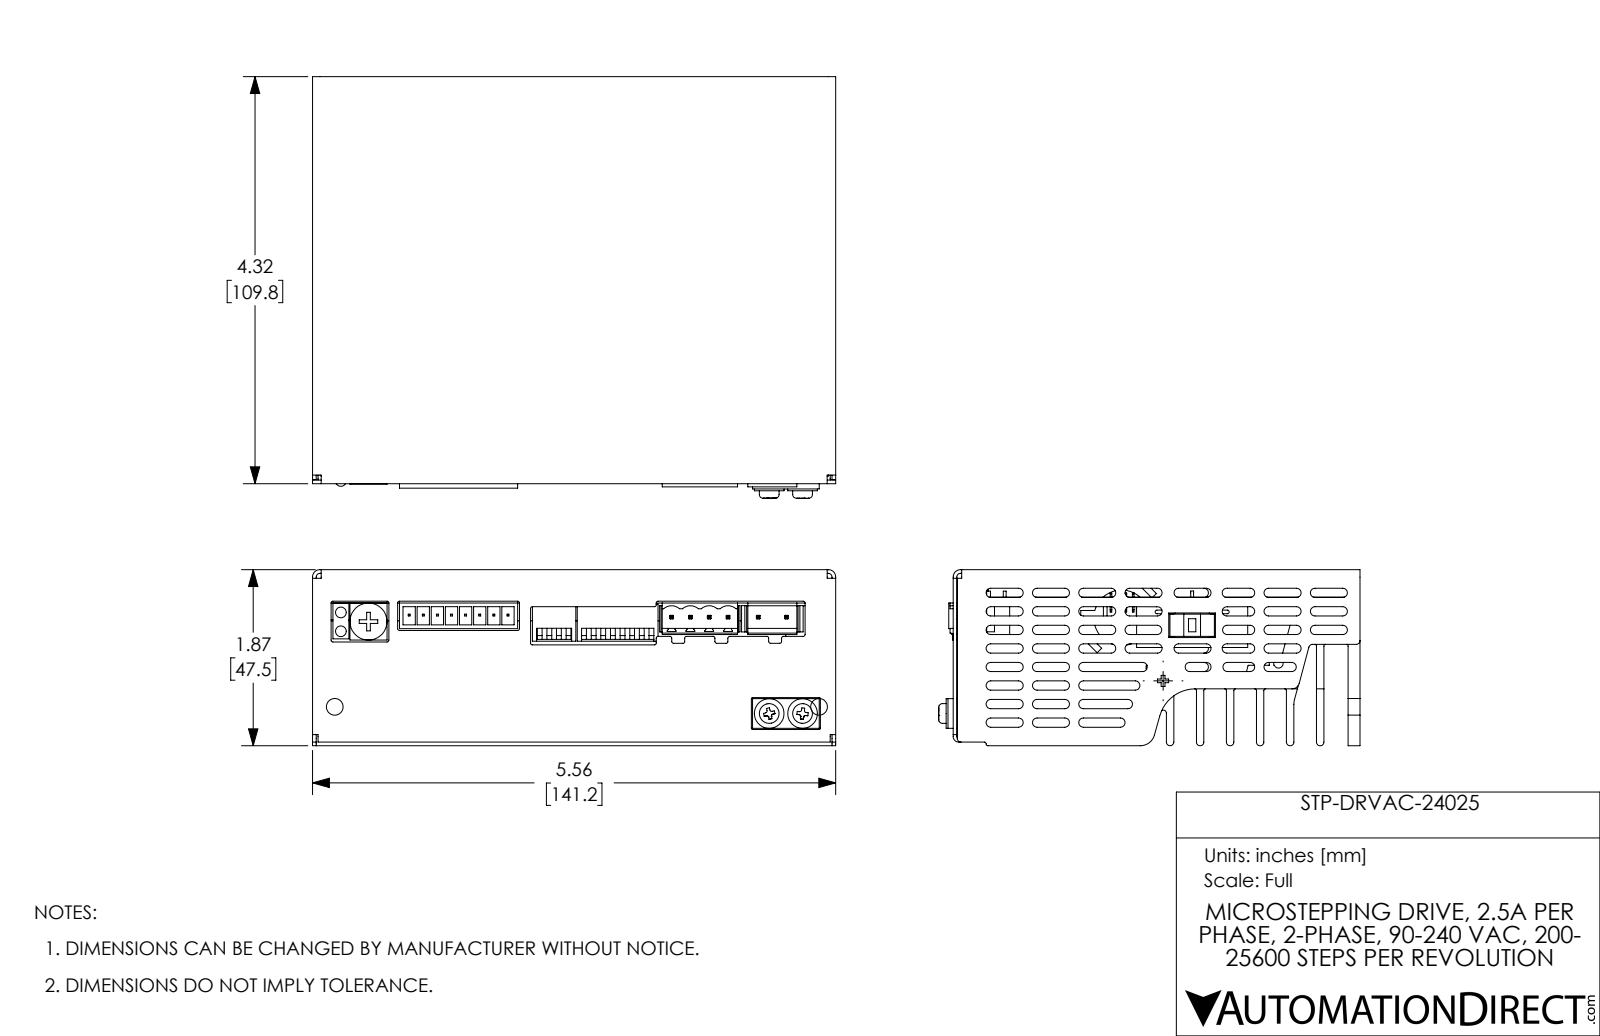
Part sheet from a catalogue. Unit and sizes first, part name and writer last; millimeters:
Units: millimetres
Overall size (bounding box): 141.2 × 113.7 × 47.5
Round holes (diameter × count): ⌀0.8 ×42, ⌀2.5 ×10, ⌀3.2 ×8, ⌀1.6 ×6, ⌀3 ×5, ⌀1 ×4, ⌀4.5 ×1, ⌀5.7 ×1, ⌀15 ×1
Round bosses / shafts (diameter × count): ⌀0.5 ×6, ⌀8 ×2, ⌀2.9 ×2, ⌀10 ×1
Partial cylindrical surfaces — rounded edges, fillets, slot ends (radius × count): R1.2 ×102, R0.5 ×90, R1 ×14, R0.2 ×10, R0.6 ×6, R0.6 ×6, R0.3 ×4, R2 ×4
Main face-to-face distances: 1, 6.4, 8.1, 2, 9, 8, 7.4, 1.6, 16.2, 24.3
Hole centre spacings: 7.6, 2.5, 8, 12.7, 5.1, 9.2, 10.8, 10.2
Volume: 200 100 mm³ · Surface area: 179 800 mm²
Bodies: 19 solids, 2517 faces (1450 planar, 708 cylindrical, 359 other)
Part name (STEP PRODUCT): STP-DRVAC-24025
STEP written by: SolidWorks 2017 (AUTOMOTIVE_DESIGN)
